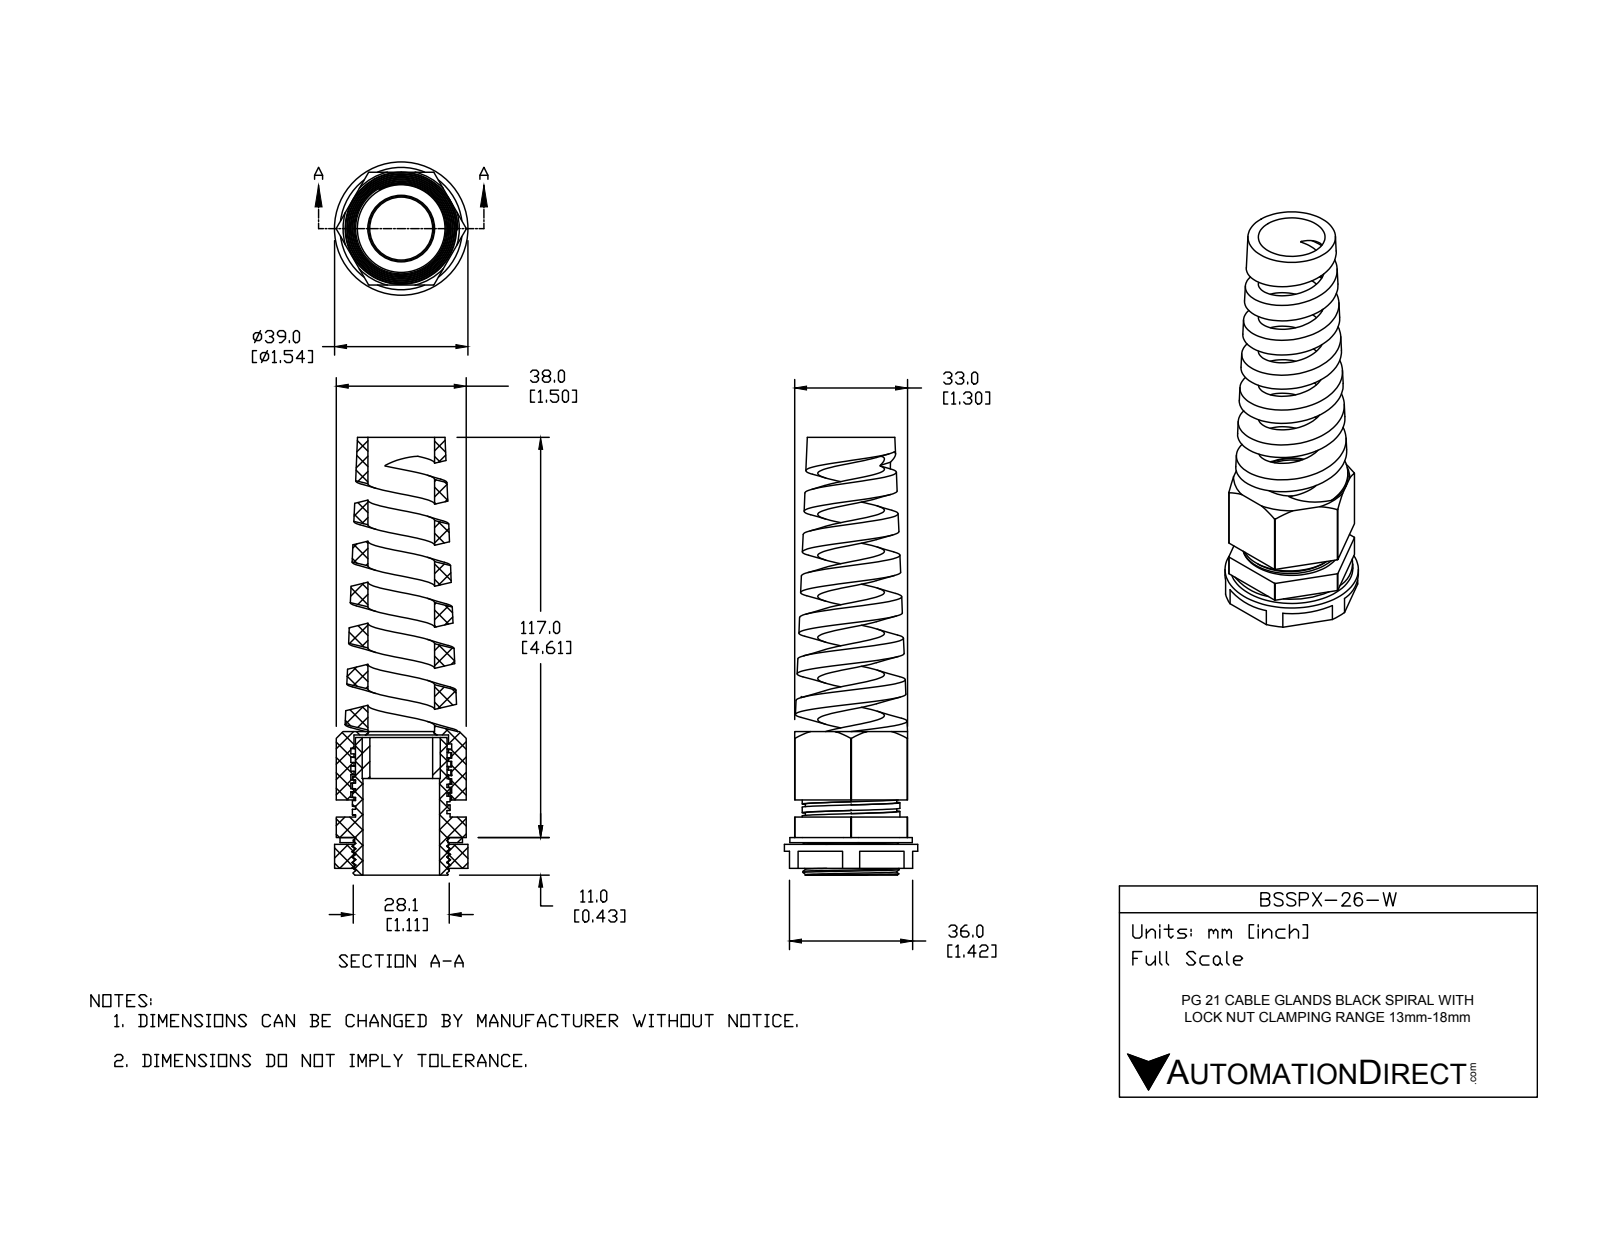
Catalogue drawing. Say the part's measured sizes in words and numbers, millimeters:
The part is named "BSSPX-26-W". Its 3-D file was written by "SolidWorks 2015 (CONFIG_CONTROL_DESIGN)". It is 5 solids with 239 faces: 105 planar, 95 cylindrical and 39 other. Overall it measures 128 by 39 by 39 millimeters. Its volume is 38 468 cubic millimeters and its surface area 33 621 square millimeters. Round holes: 1 of diameter 18.4, 1 of diameter 19.5, 1 of diameter 22.4, 1 of diameter 22.8, 1 of diameter 27.2, 1 of diameter 27.34, 1 of diameter 27.67. Round bosses or shafts: 1 of diameter 39, 1 of diameter 35.8, 1 of diameter 28.6, 1 of diameter 28.1, 1 of diameter 26.8. Partial cylindrical surfaces (rounded edges, fillets, slot ends): 1 of radius 19. The main face-to-face distances are 33, 1.5, 1, 9.5, 32.5, 2.5, 34.5, 8.5, 7, 11.
